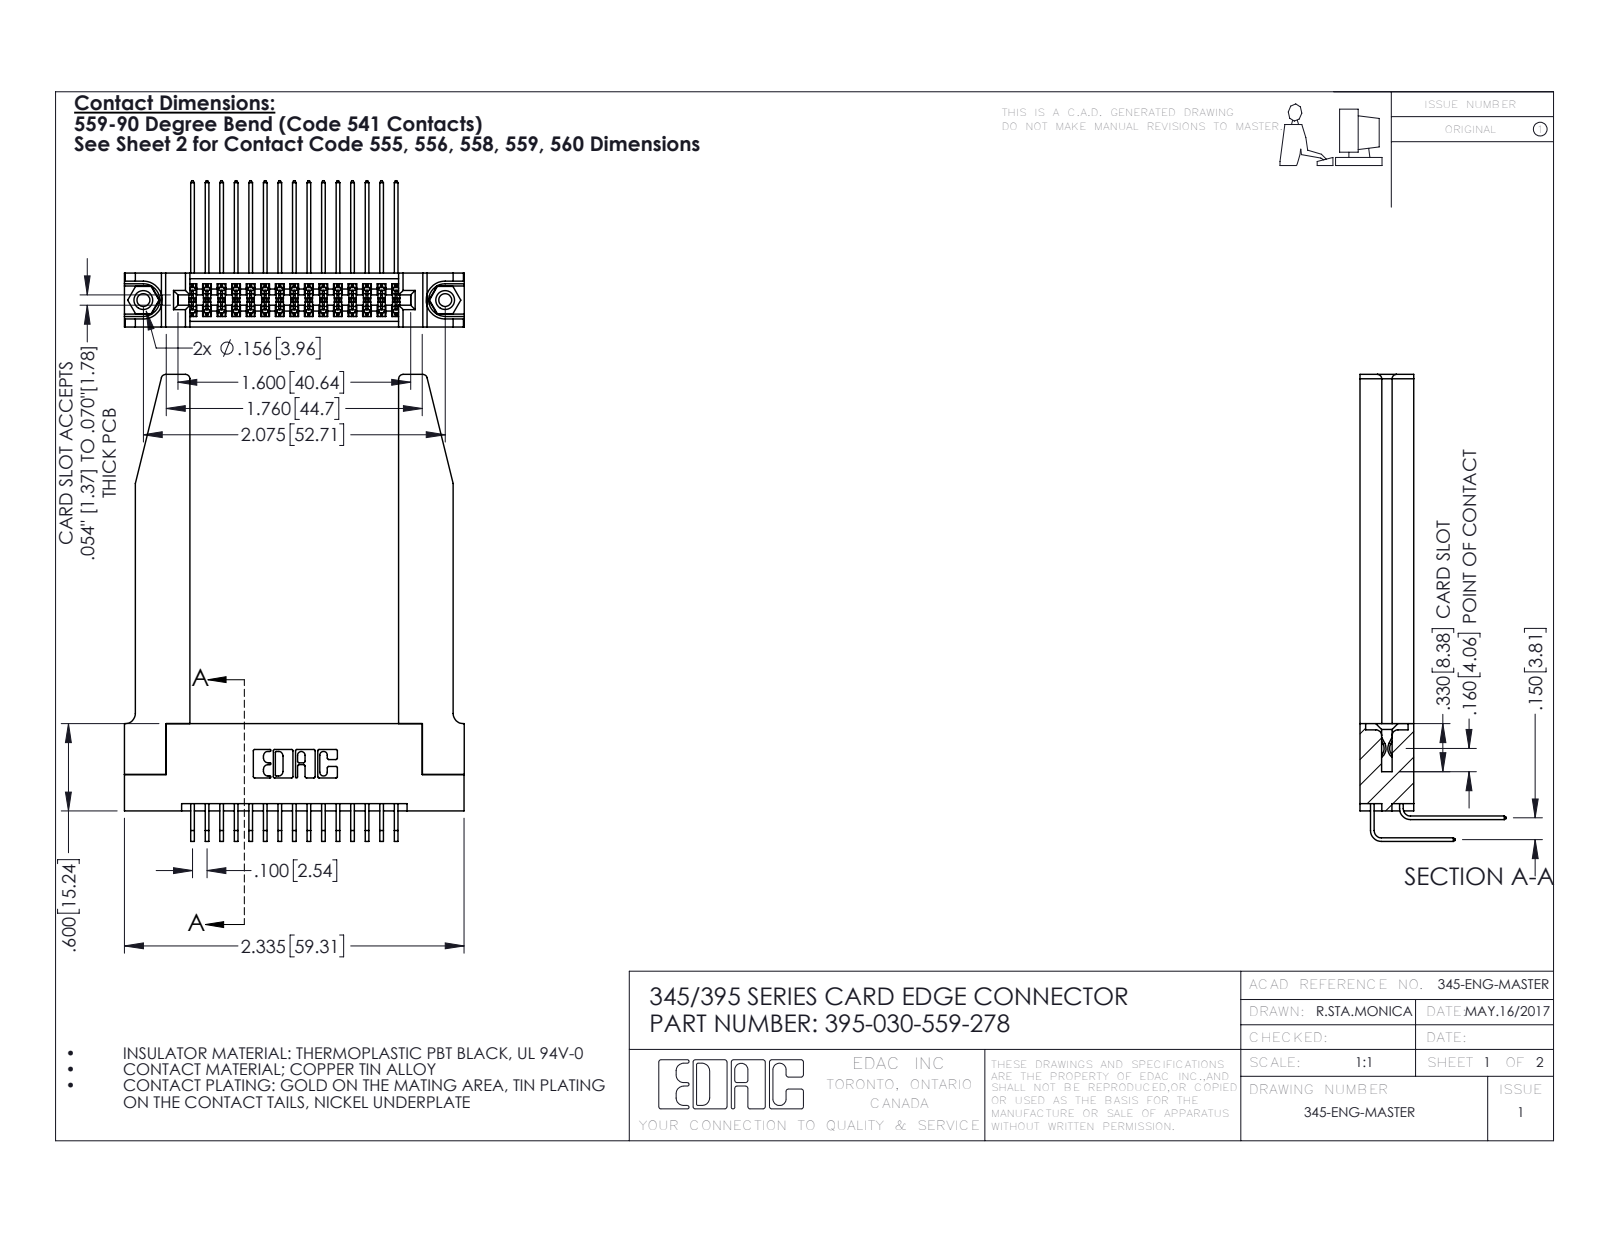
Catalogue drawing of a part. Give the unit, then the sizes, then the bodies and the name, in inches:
Units: inches
Overall size (bounding box): 3.209 × 2.336 × 1.005
Round holes (diameter × count): ⌀0.089 ×2, ⌀0.125 ×2, ⌀0.156 ×2, ⌀0.064 ×1
Round bosses / shafts (diameter × count): ⌀0.155 ×2
Partial cylindrical surfaces — rounded edges, fillets, slot ends (radius × count): R0.006 ×45, R0.01 ×22, R0.03 ×8, R0.007 ×6, R0.031 ×6, R0.026 ×3, R0.014 ×2, R0.019 ×2
Main face-to-face distances: 0.37, 0.072, 0.298, 0.2, 0.15, 0.148, 0.098, 0.272, 0.025, 0.077
Hole centre spacings: 0.27, 1.842, 2.075
Volume: 0.821 in³ · Surface area: 24.08 in²
Bodies: 35 solids, 1920 faces (1272 planar, 596 cylindrical, 52 other)
Part name (STEP PRODUCT): 345-220-078_345-220-078; 345-250-001_345-250-001-102; 345-292-001_558 559 Tail - 1; 345-292-001_559 Tail - 2 (+2 more)
STEP written by: SolidWorks 2016 (CONFIG_CONTROL_DESIGN)
